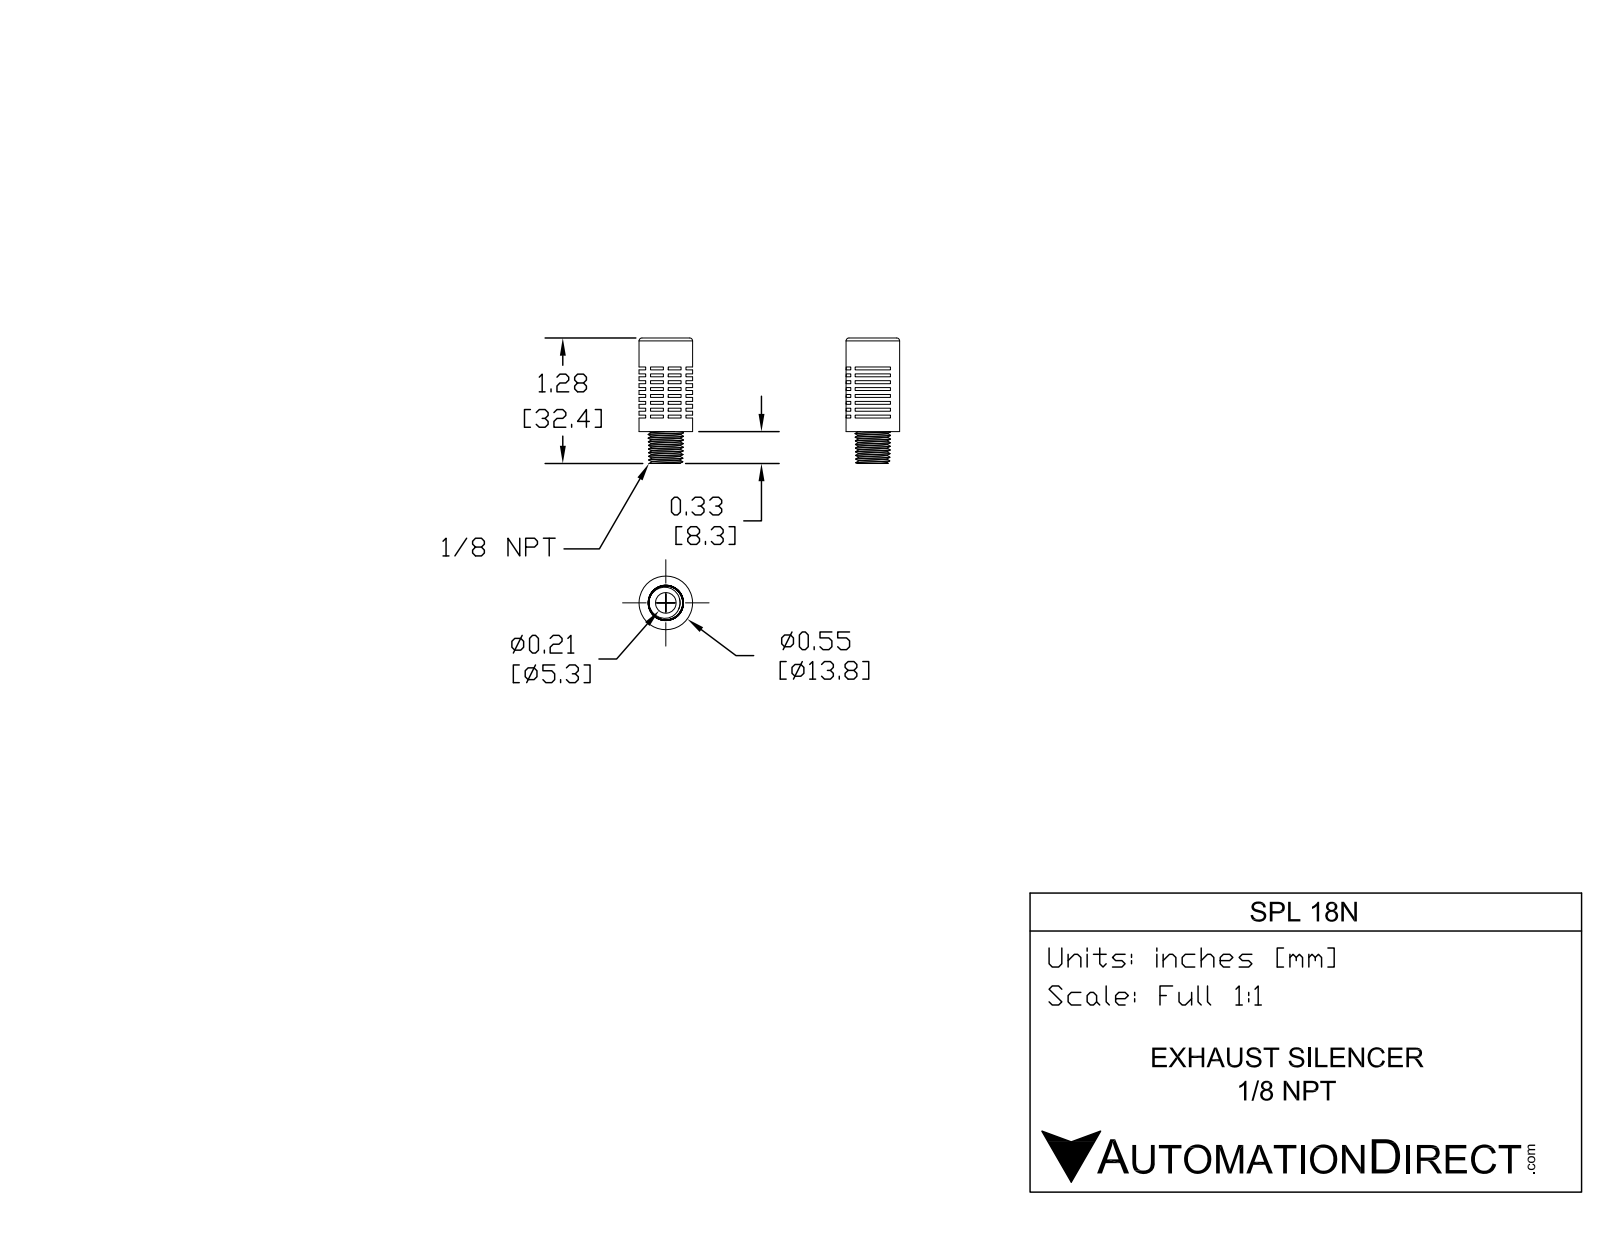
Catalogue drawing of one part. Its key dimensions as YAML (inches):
part_name: "SPL-18N"
step_written_by: "SolidWorks 2015 (CONFIG_CONTROL_DESIGN)"
units: inches
bodies: {solids: 1, faces: 178, planar: 149, cylindrical: 4, other: 25}
overall_size: [1.277, 0.545, 0.545]
volume: 0.179
surface_area: 5.721
round_holes:
  - {diameter: 0.21, count: 1}
round_bosses_or_shafts:
  - {diameter: 0.545, count: 1}
face_to_face_distances: [0.07, 0.03, 0.14, 0.21, 0.28, 0.1, 0.35, 0.04, 0.18, 0.14]
